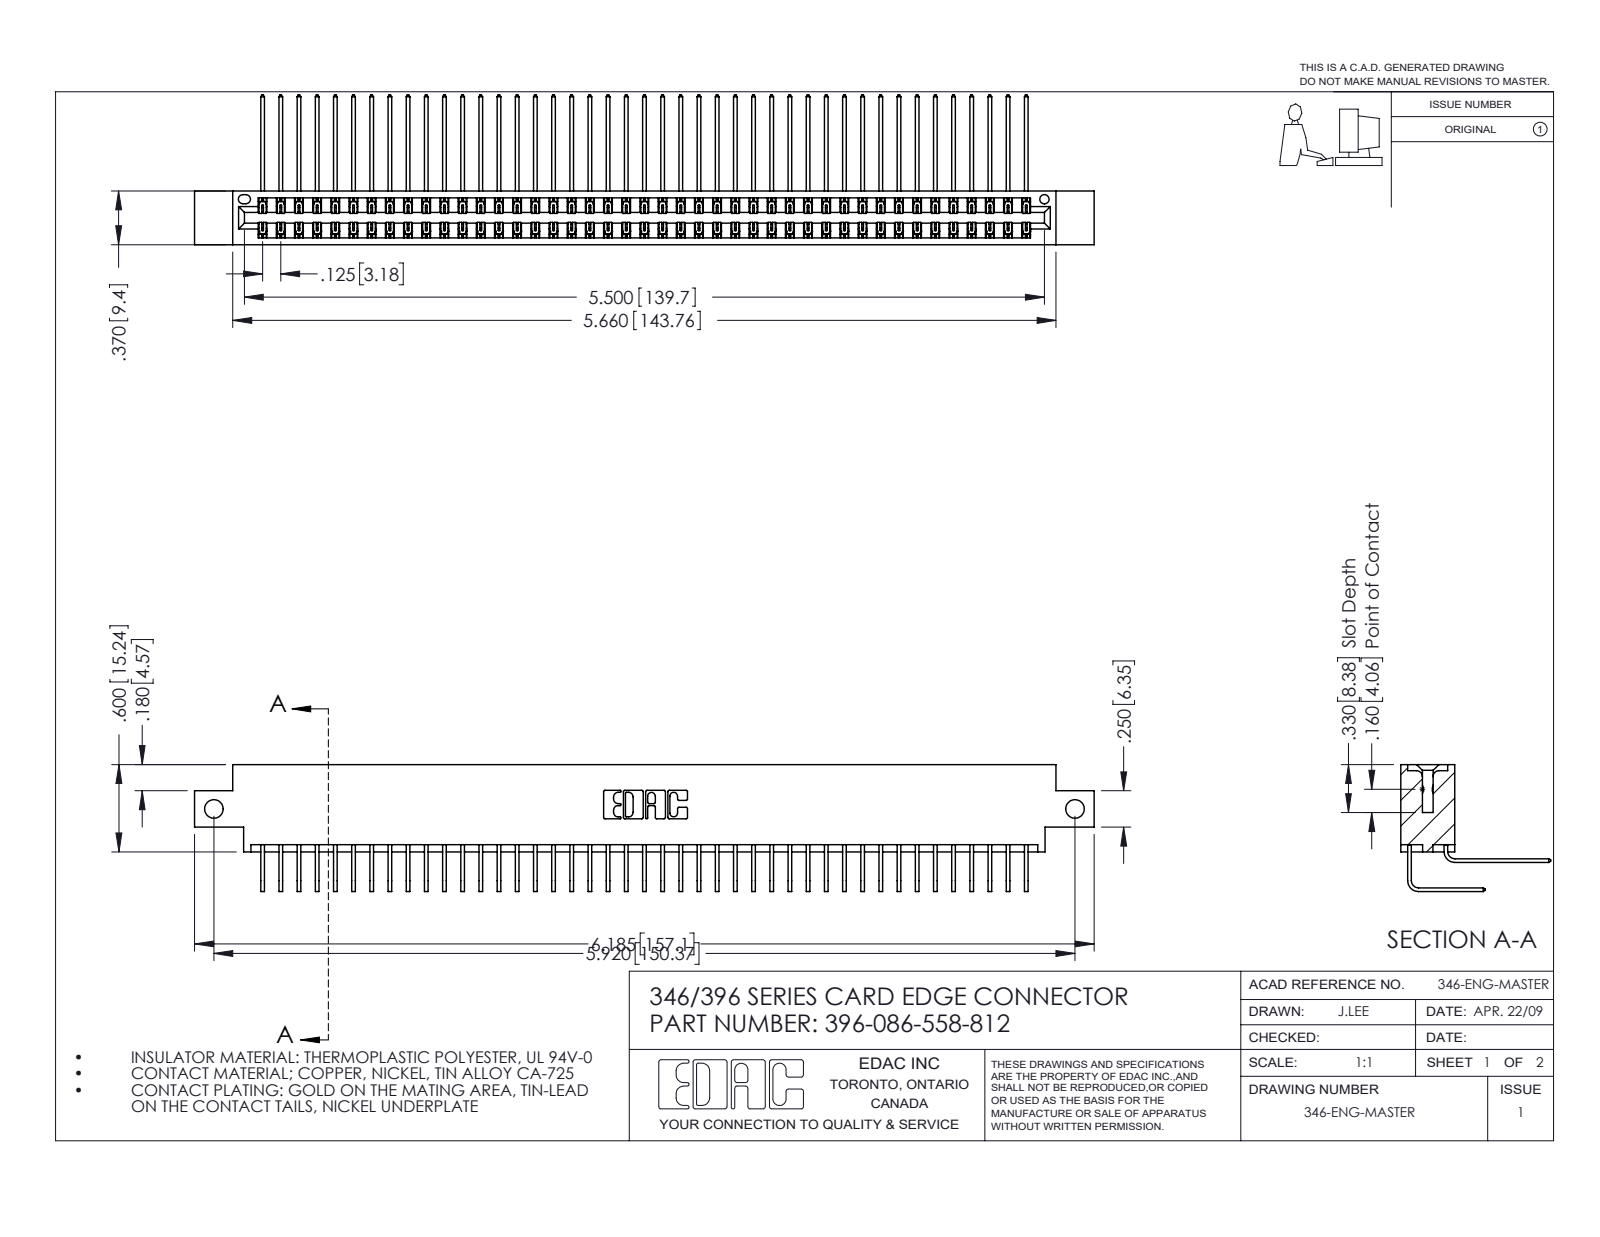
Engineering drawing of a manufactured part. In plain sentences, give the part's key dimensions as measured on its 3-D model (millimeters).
The part is named "345-292-001_558 559 Tail - 1; 346 Part_0.170 Offset - Side Mount; 396-086-558-812; 345-292-001_558 Tail - 2". Its 3-D file was written by "SolidWorks 2016 (CONFIG_CONTROL_DESIGN)". It is 87 solids with 4770 faces: 3262 planar, 1508 cylindrical and 0 other. Overall it measures 157.1 by 26.2 by 22.2 millimeters. Its volume is 15 600 cubic millimeters and its surface area 23 860 square millimeters. Round holes: 2 of diameter 3.3, 1 of diameter 1.6. Partial cylindrical surfaces (rounded edges, fillets, slot ends): 129 of radius 0.2, 22 of radius 0.3, 6 of radius 0.2, 6 of radius 0.8, 3 of radius 0.7, 2 of radius 0.4, 2 of radius 0.6, 2 of radius 0.6. The main face-to-face distances are 8.2, 1.2, 0.6, 9.4, 6.4, 7.6, 1.8, 7, 3.8, 5.6. The hole center spacings are 150.4.
